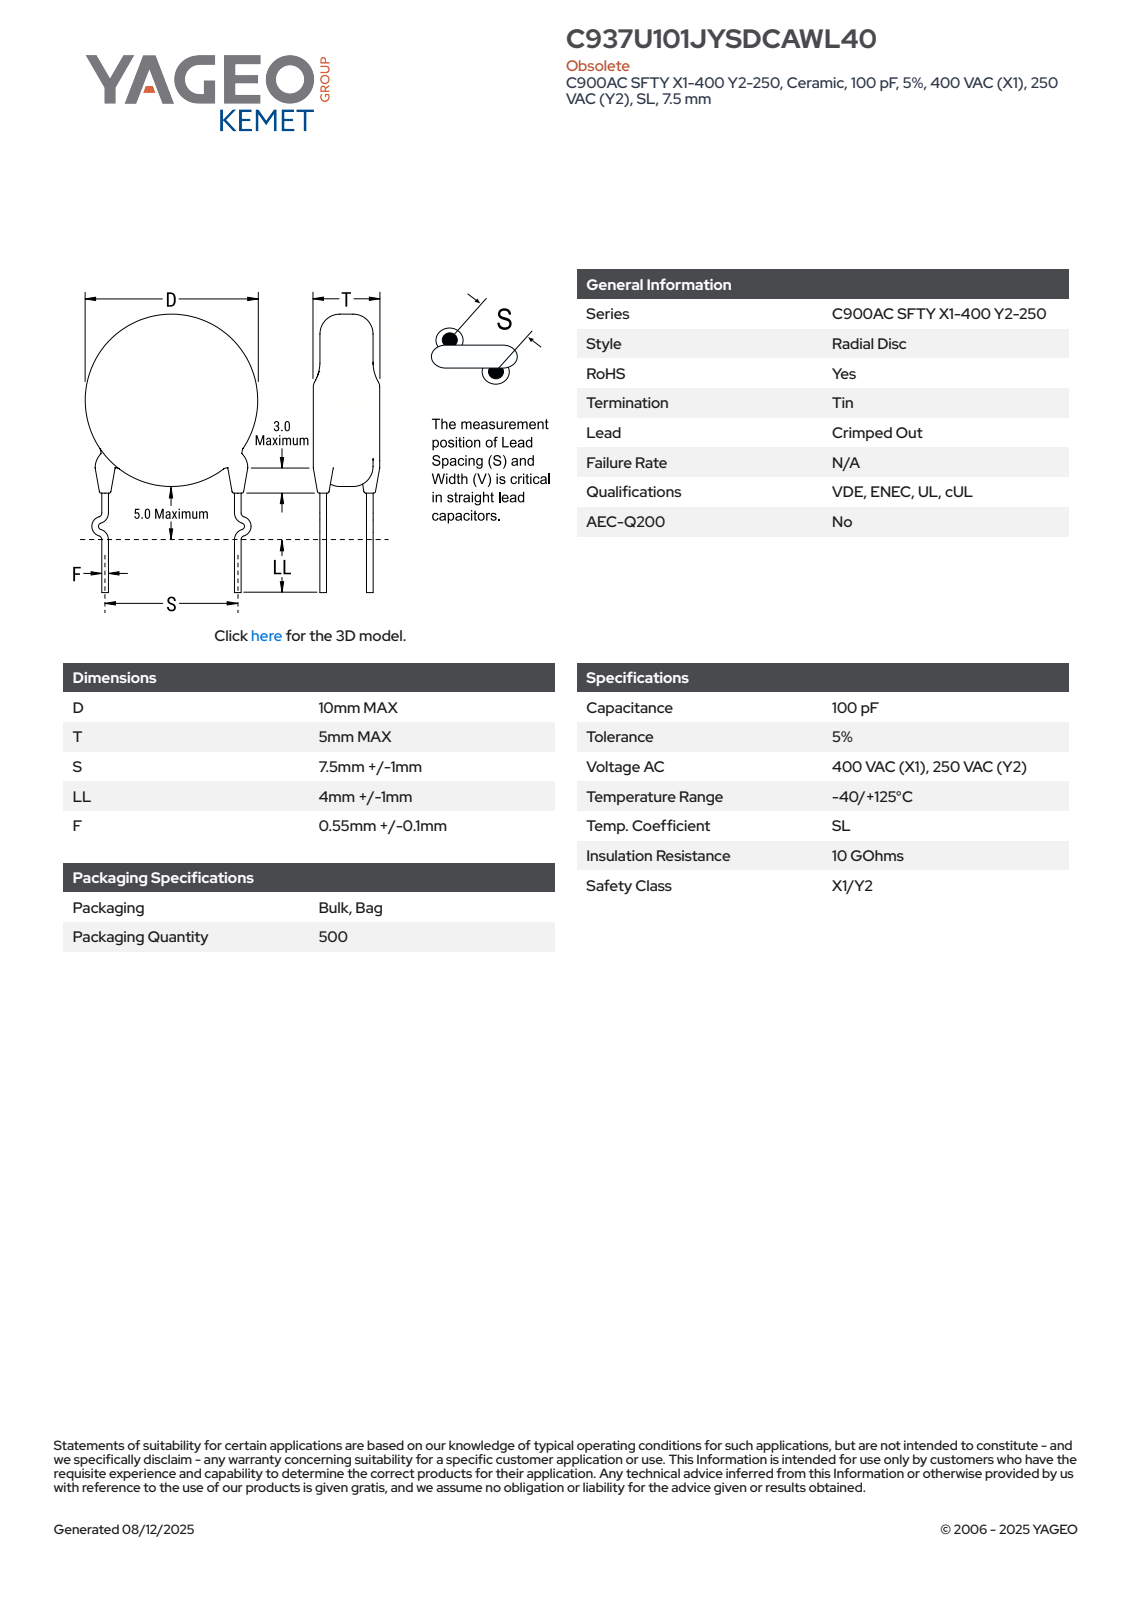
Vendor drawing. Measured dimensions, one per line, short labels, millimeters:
name: CCD_KCOC900_D10T5S7.5LL5F0.55
written by: SolidWorks 2014 (AUTOMOTIVE_DESIGN)
unit: mm
bodies: 4 solids, 85 faces (63 planar, 6 cylindrical, 16 other)
size: 20 × 12.44 × 5
volume: 391 mm³; area: 354 mm²
bosses: 2× ⌀1.2, 1× ⌀10
face distances: 5, 1.04, 5.53, 4.49, 0.84, 4.24, 0.38, 4.52, 3.08, 3.2
